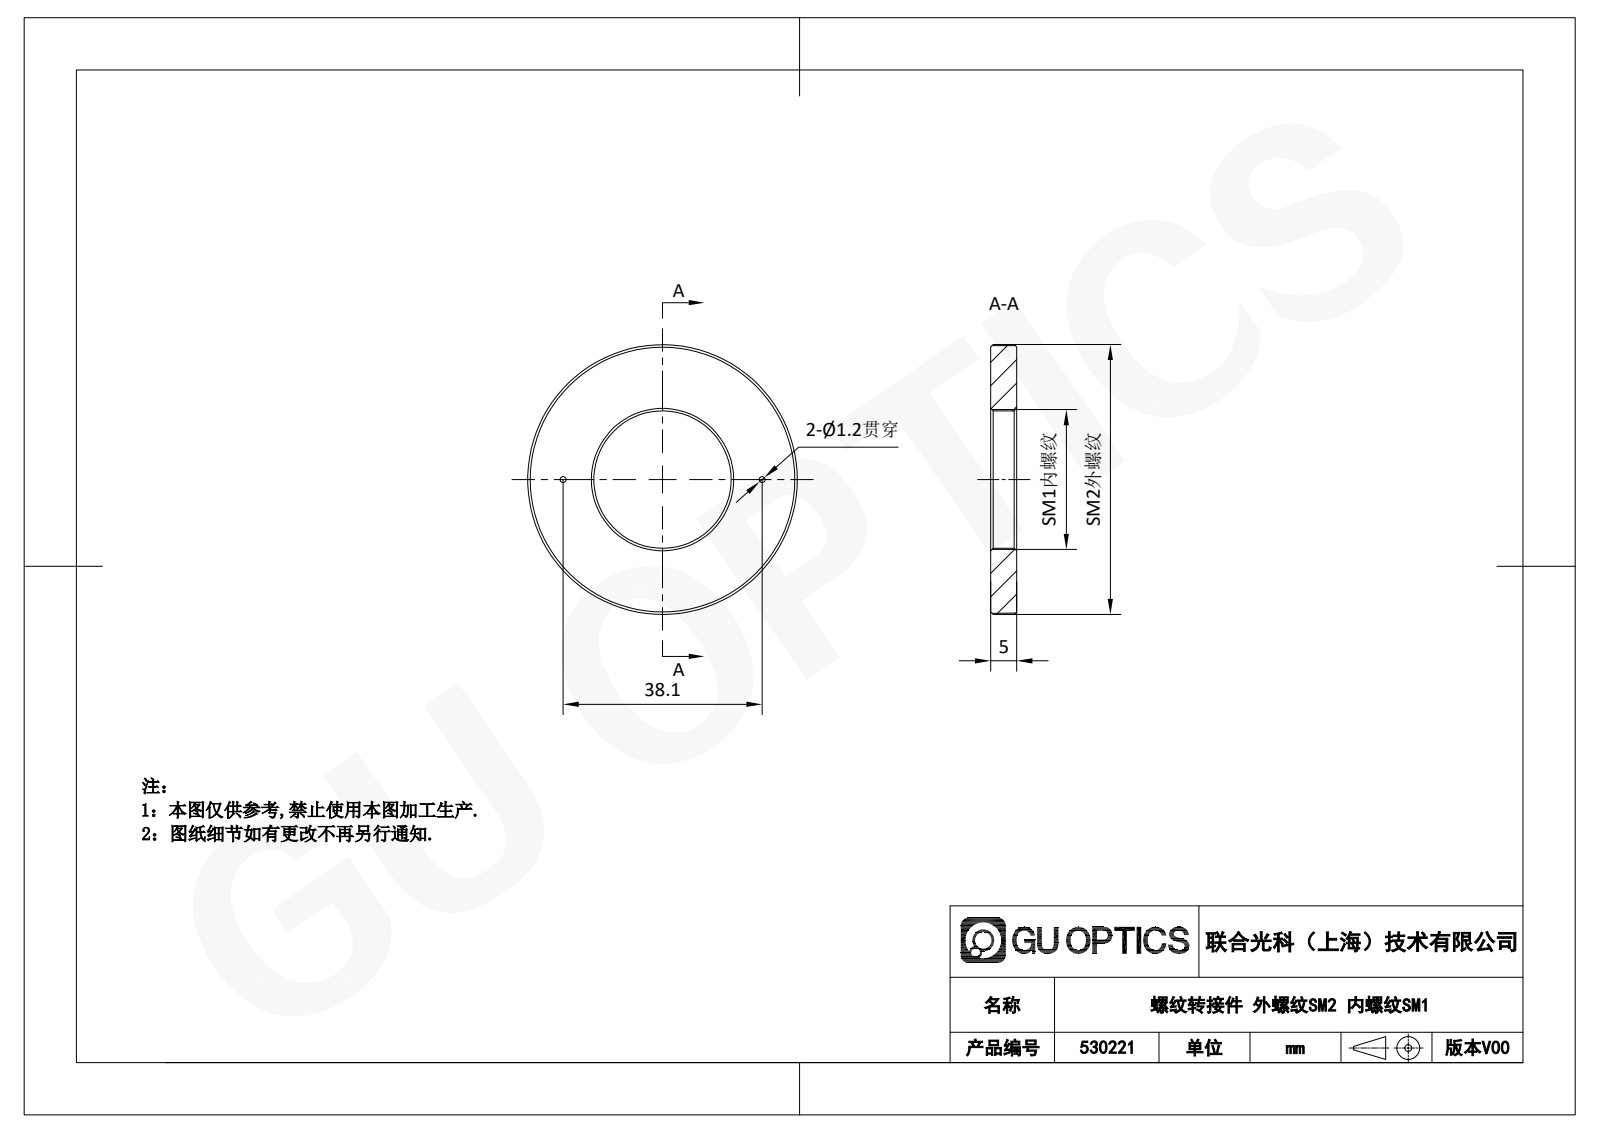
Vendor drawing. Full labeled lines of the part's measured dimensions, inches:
Part name (STEP PRODUCT): 530221
STEP written by: SolidWorks 2020 (CONFIG_CONTROL_DESIGN)
Units: inches
Bodies: 1 solid, 10 faces (2 planar, 4 cylindrical, 4 other)
Overall size (bounding box): 2.035 × 2.035 × 0.197
Volume: 0.47 in³ · Surface area: 6.55 in²
Round holes (diameter × count): ⌀0.047 ×2, ⌀1.035 ×1
Round bosses / shafts (diameter × count): ⌀2.035 ×1
Main face-to-face distances: 0.197
Hole centre spacings: 0.75, 1.5
